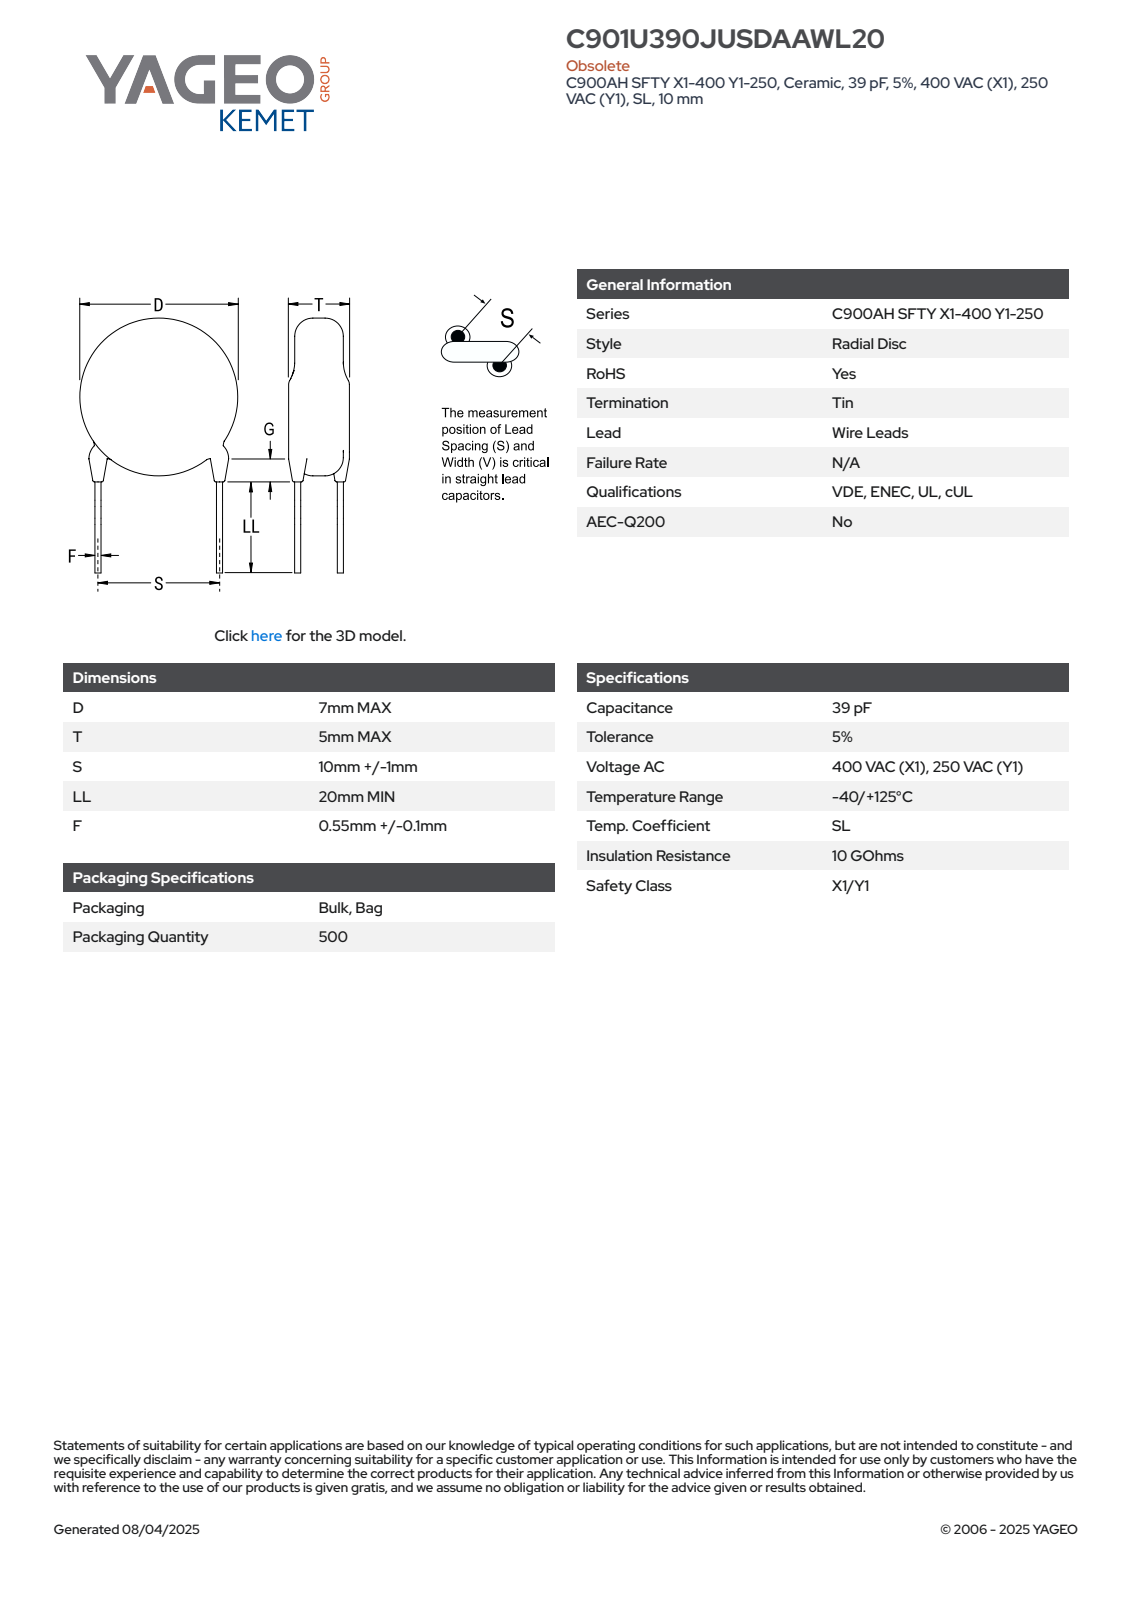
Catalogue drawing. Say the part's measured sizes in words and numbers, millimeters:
The part is named "CCD_STC900_D7T5S10LL20F0.65G3". Its 3-D file was written by "SolidWorks 2014 (AUTOMOTIVE_DESIGN)". It is 4 solids with 83 faces: 61 planar, 6 cylindrical and 16 other. Overall it measures 27.45 by 10.02 by 5 millimeters. Its volume is 202 cubic millimeters and its surface area 270 square millimeters. Round bosses or shafts: 2 of diameter 0.65, 1 of diameter 7. The main face-to-face distances are 5, 0.81, 24.35, 23.54, 3.3, 1.67, 3.52, 2.4, 2.49, 1.32.
